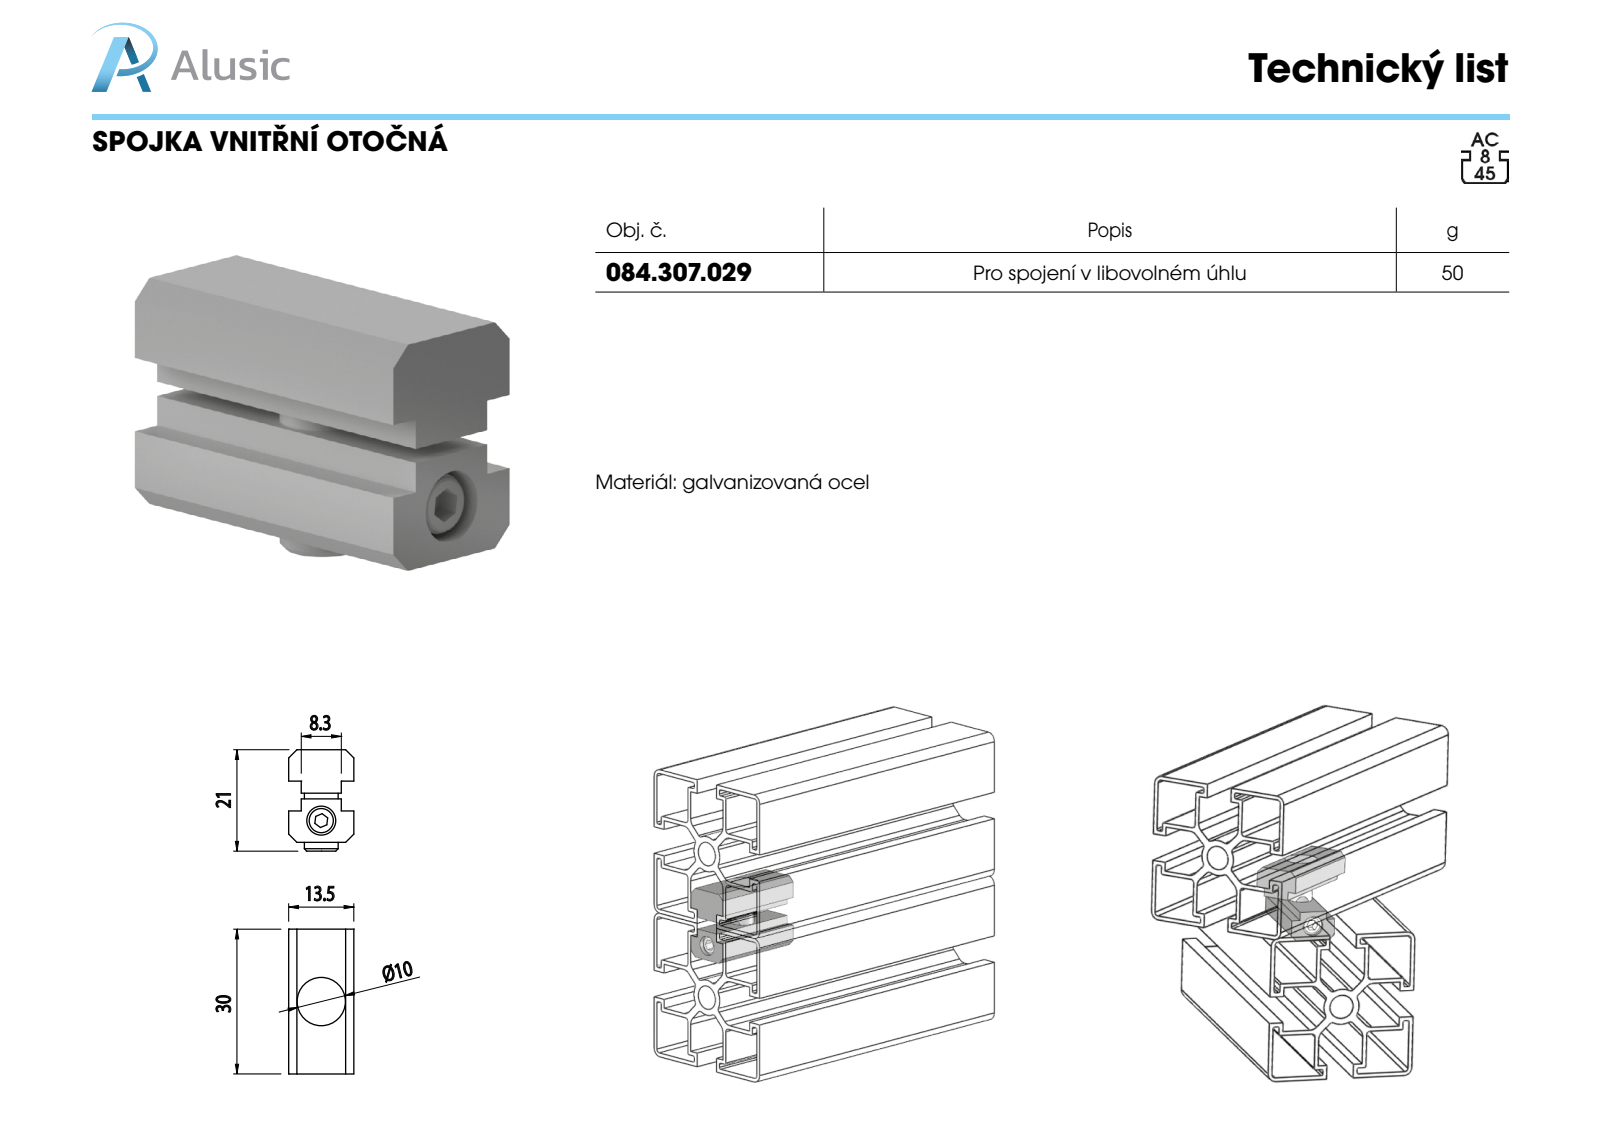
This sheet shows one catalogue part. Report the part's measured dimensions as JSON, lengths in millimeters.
{"part_name": "084.307.028A; 084.307.029; Socket Set Screw Cup Point_ALUSIC_PreviewCfg; 084.307.029C (+1 more)", "step_written_by": "SolidWorks 2011 (CONFIG_CONTROL_DESIGN)", "units": "millimeters", "bodies": {"solids": 4, "faces": 129, "planar": 35, "cylindrical": 34, "other": 60}, "overall_size": [30, 21, 13.5], "volume_mm3": 6360, "surface_area_mm2": 4451, "round_holes": [[7, 1], [10, 1]], "round_bosses_or_shafts": [[6, 1]], "face_to_face_distances": [10.18, 9, 6.5, 2.5, 12.68, 3.68, 2.6, 10.9, 13.5, 19.18]}
